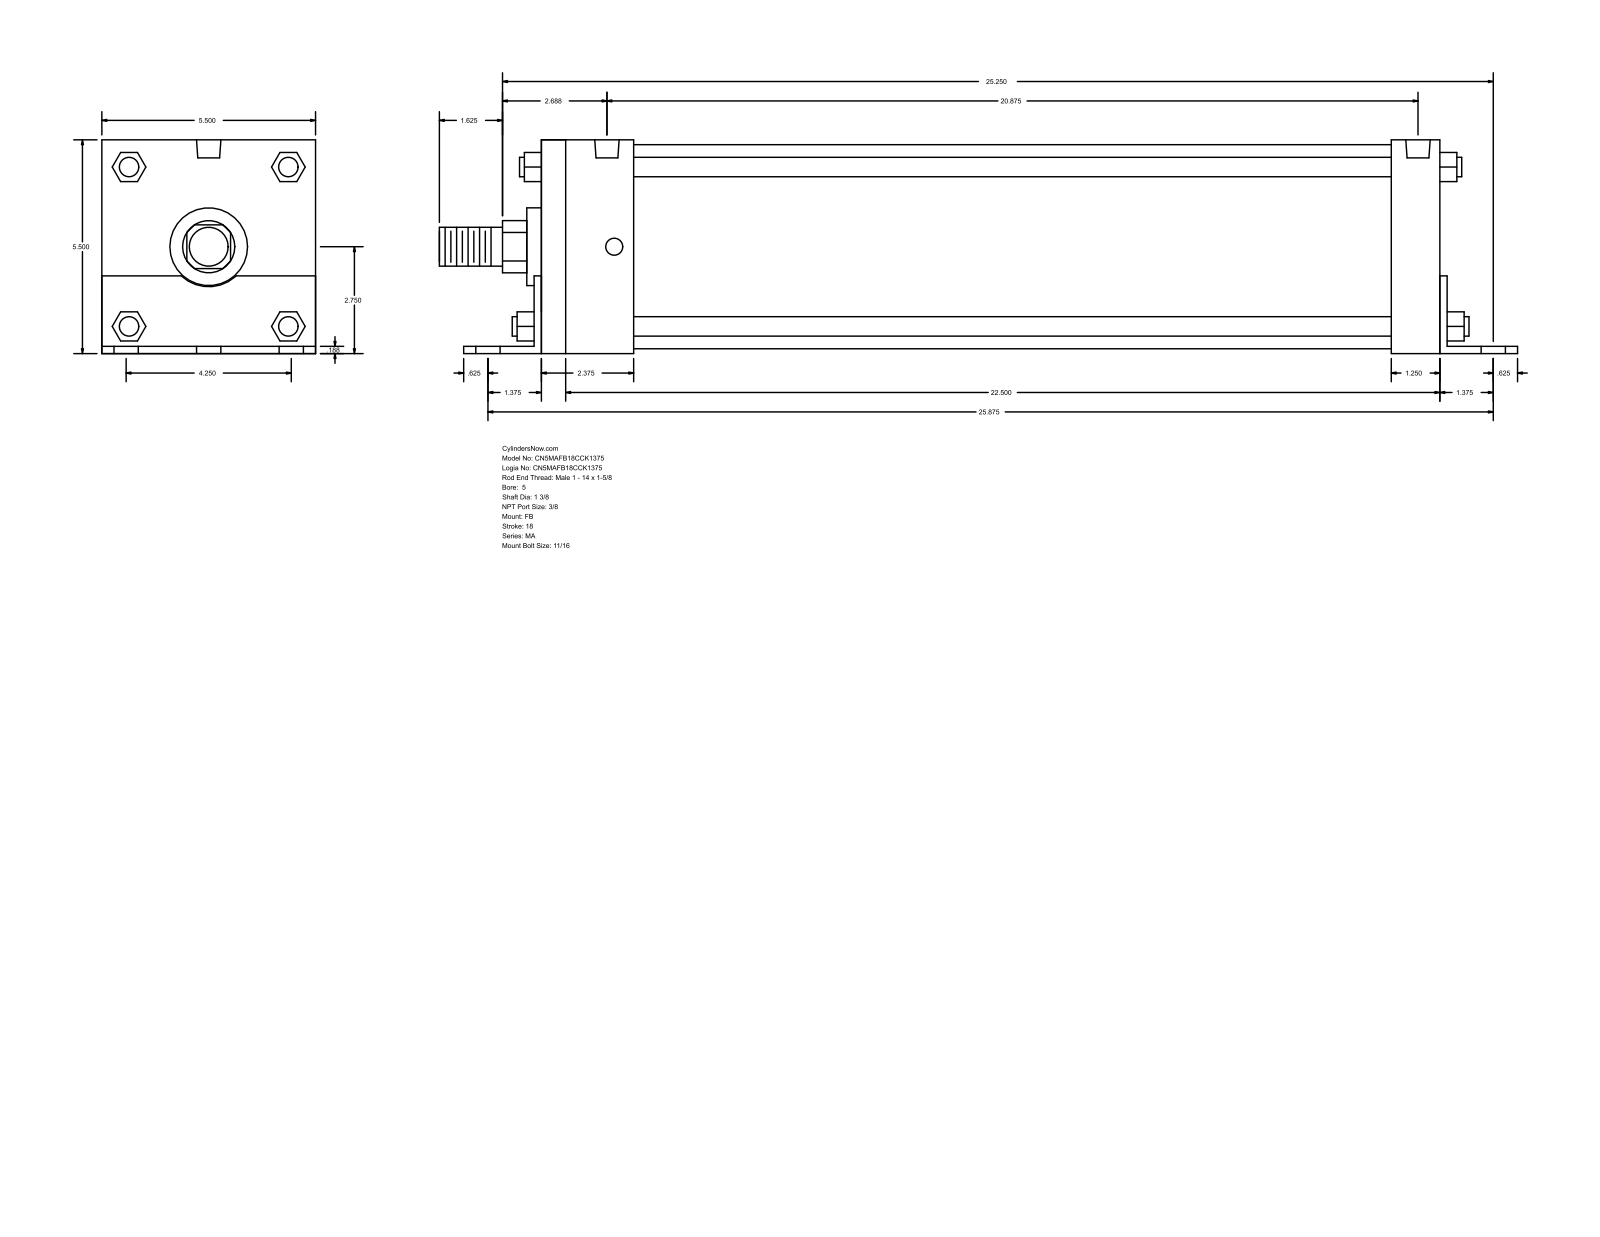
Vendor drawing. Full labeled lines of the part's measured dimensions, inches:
Part name (STEP PRODUCT): MA_FB__0500_1.375
STEP written by: GSSL Pune (CONFIG_CONTROL_DESIGN)
Units: inches
Bodies: 0 solids, 140 faces (105 planar, 35 cylindrical, 0 other)
Overall size (bounding box): 27.75 × 5.502 × 5.5
Round holes (diameter × count): ⌀0.687 ×6, ⌀0.437 ×4, ⌀0.627 ×2
Round bosses / shafts (diameter × count): ⌀0.5 ×4, ⌀5.25 ×1, ⌀2 ×1, ⌀1.375 ×1, ⌀1 ×1
Partial cylindrical surfaces — rounded edges, fillets, slot ends (radius × count): R0.672 ×1, R1.03 ×1
Main face-to-face distances: 5.5, 0.187, 5.502, 0.185, 5.315, 23.125, 0.188, 23.313, 23.312, 23.5
Hole centre spacings: 2.125, 25.962, 25.875, 2.876, 3.005, 3.728, 3.883, 4.25
